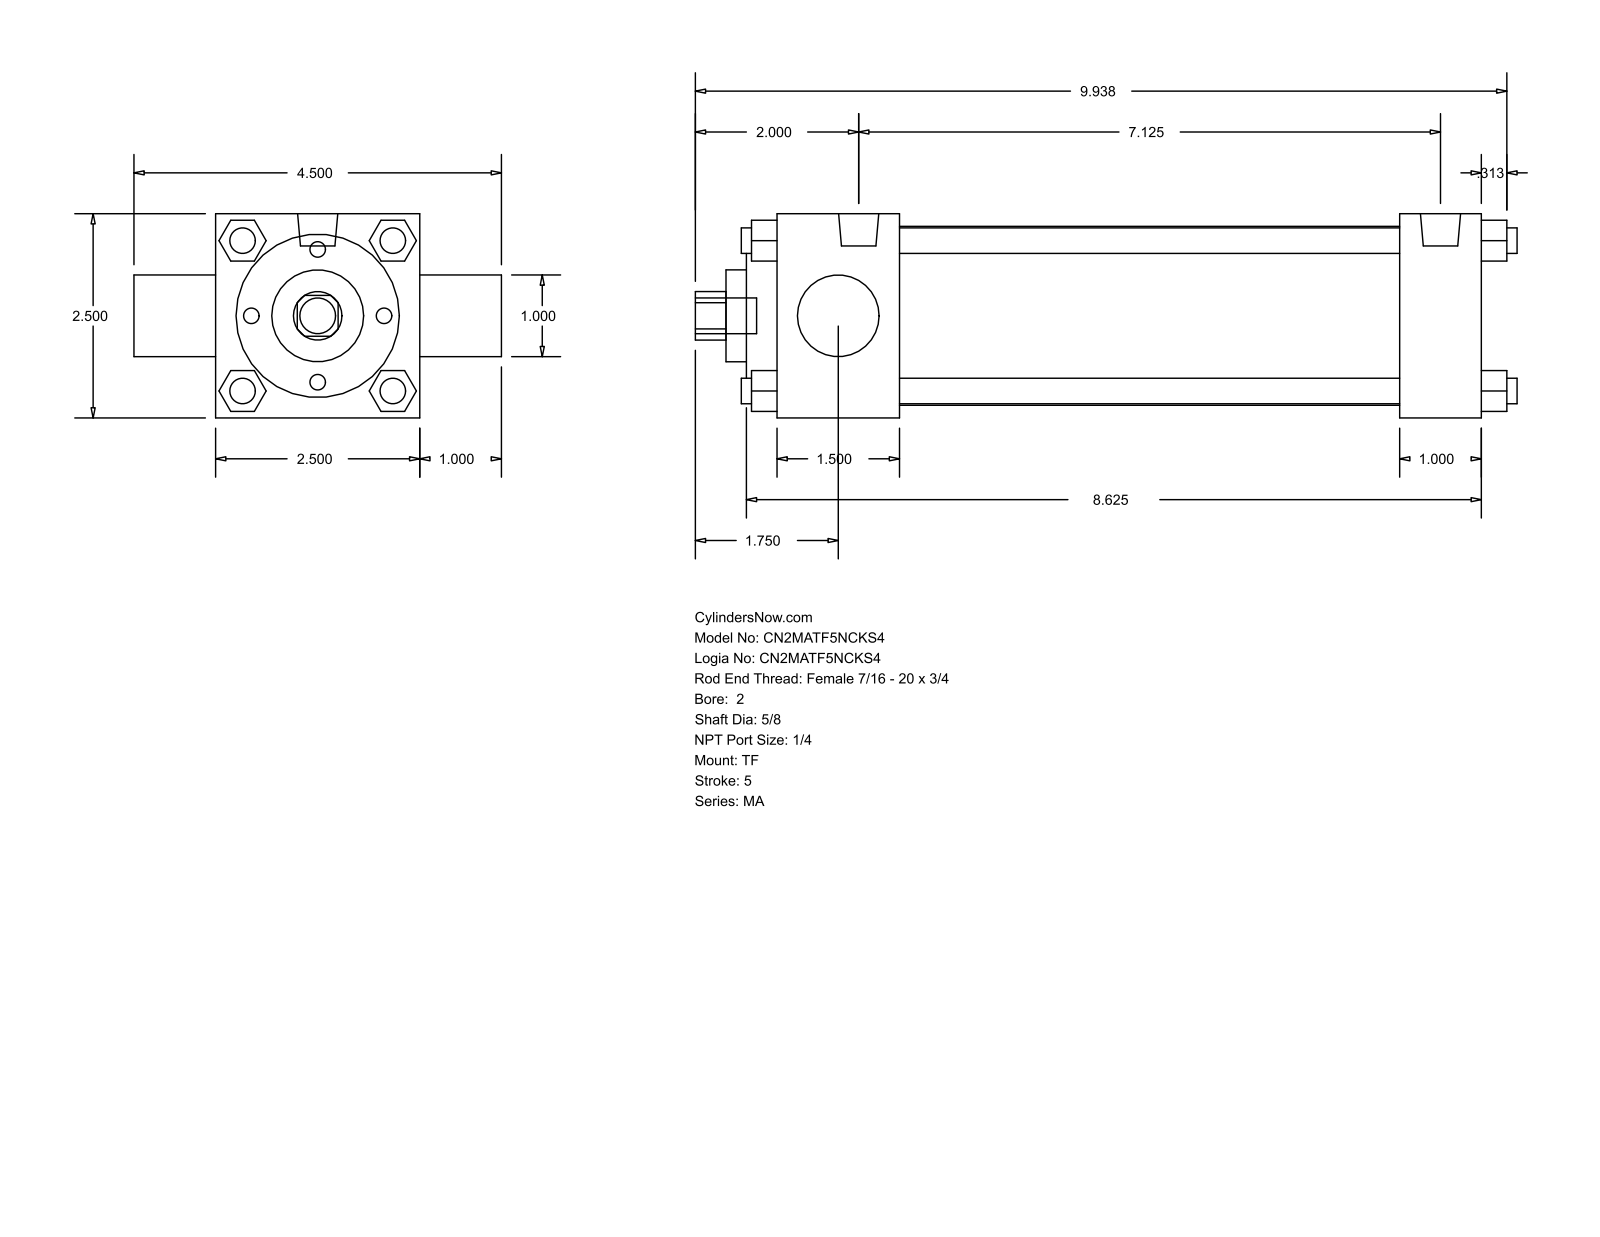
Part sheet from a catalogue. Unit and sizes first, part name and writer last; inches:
Units: inches
Overall size (bounding box): 10.063 × 4.5 × 2.5
Round holes (diameter × count): ⌀0.625 ×1, ⌀1 ×1, ⌀1.125 ×1, ⌀2 ×1, ⌀2.19 ×1
Round bosses / shafts (diameter × count): ⌀0.313 ×7, ⌀0.492 ×2, ⌀0.437 ×1
Partial cylindrical surfaces — rounded edges, fillets, slot ends (radius × count): R0.297 ×1
Main face-to-face distances: 2.5, 1, 1.5, 0.5, 8.625, 0.375, 7.625, 6.125, 7.125, 1.875
Bodies: 0 solids, 122 faces (93 planar, 29 cylindrical, 0 other)
Part name (STEP PRODUCT): MA_TF__0200_0.625
STEP written by: GSSL Pune (CONFIG_CONTROL_DESIGN)
